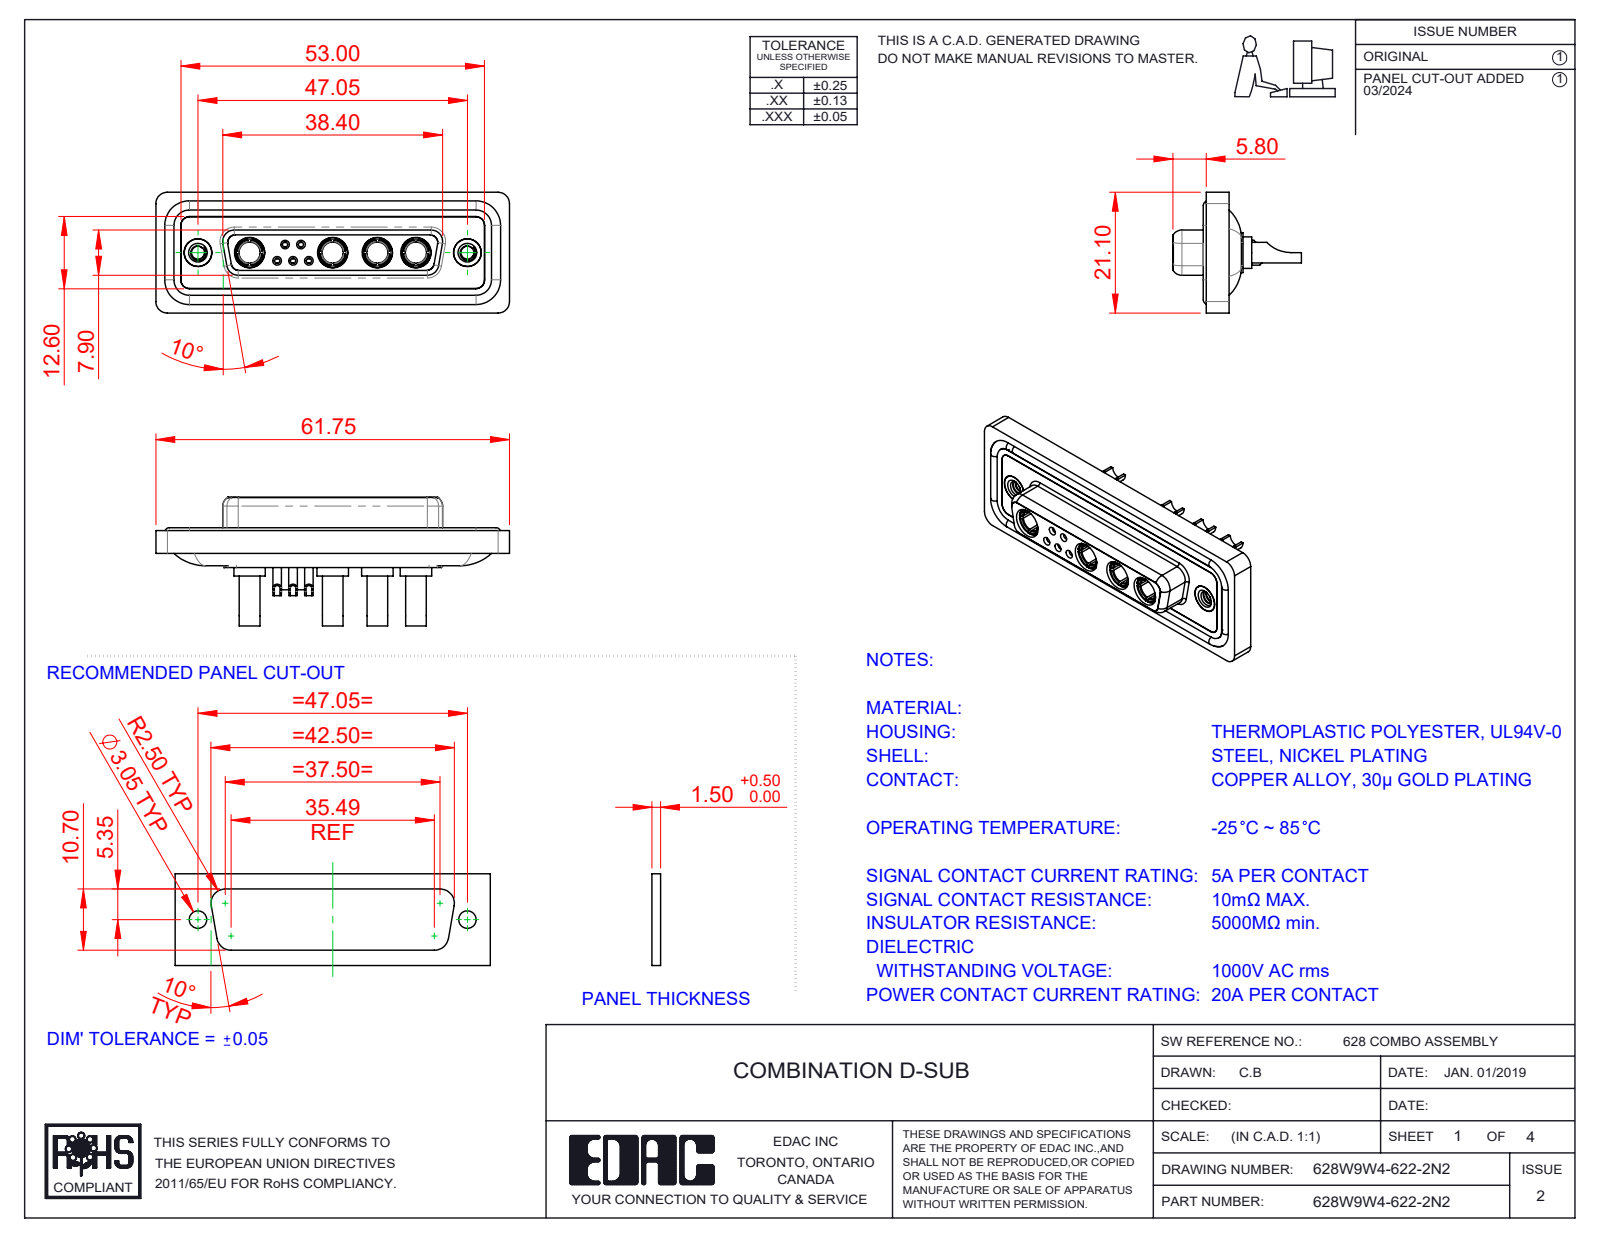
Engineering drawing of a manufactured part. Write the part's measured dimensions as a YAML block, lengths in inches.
part_name: "628Combo Contact Row 2_22; 628Combo Contact Row 1_22; 628Combo Threaded Rivet_2; 628Combo Shell Rear_25 Contacts (+5 more)"
step_written_by: "SolidWorks 2023 (CONFIG_CONTROL_DESIGN)"
units: inches
bodies: {solids: 20, faces: 981, planar: 318, cylindrical: 397, other: 266}
overall_size: [2.431, 0.884, 0.831]
volume: 0.506
surface_area: 21.62
round_holes:
  - {diameter: 0.191, count: 6}
  - {diameter: 0.035, count: 5}
  - {diameter: 0.039, count: 5}
  - {diameter: 0.043, count: 5}
  - {diameter: 0.059, count: 5}
  - {diameter: 0.079, count: 5}
  - {diameter: 0.106, count: 4}
  - {diameter: 0.146, count: 4}
  - {diameter: 0.209, count: 4}
  - {diameter: 0.063, count: 3}
  - {diameter: 0.067, count: 2}
  - {diameter: 0.089, count: 2}
round_bosses_or_shafts:
  - {diameter: 0.063, count: 6}
  - {diameter: 0.087, count: 5}
  - {diameter: 0.217, count: 4}
  - {diameter: 0.205, count: 4}
  - {diameter: 0.195, count: 4}
  - {diameter: 0.187, count: 4}
  - {diameter: 0.148, count: 4}
  - {diameter: 0.142, count: 4}
partial_cylinders:
  - {radius: 0.059, count: 22}
  - {radius: 0.079, count: 18}
  - {radius: 0.053, count: 8}
  - {radius: 0.063, count: 8}
  - {radius: 0.039, count: 6}
  - {radius: 0.01, count: 4}
  - {radius: 0.02, count: 4}
  - {radius: 0.024, count: 4}
face_to_face_distances: [0.016, 0.071, 0.293, 0.222, 0.02, 0.278, 0.26, 0.063, 0.043, 0.114]
hole_center_spacings: [0.124, 0.109, 0.198, 0.109, 0.173, 0.198, 0.218, 0.226]
